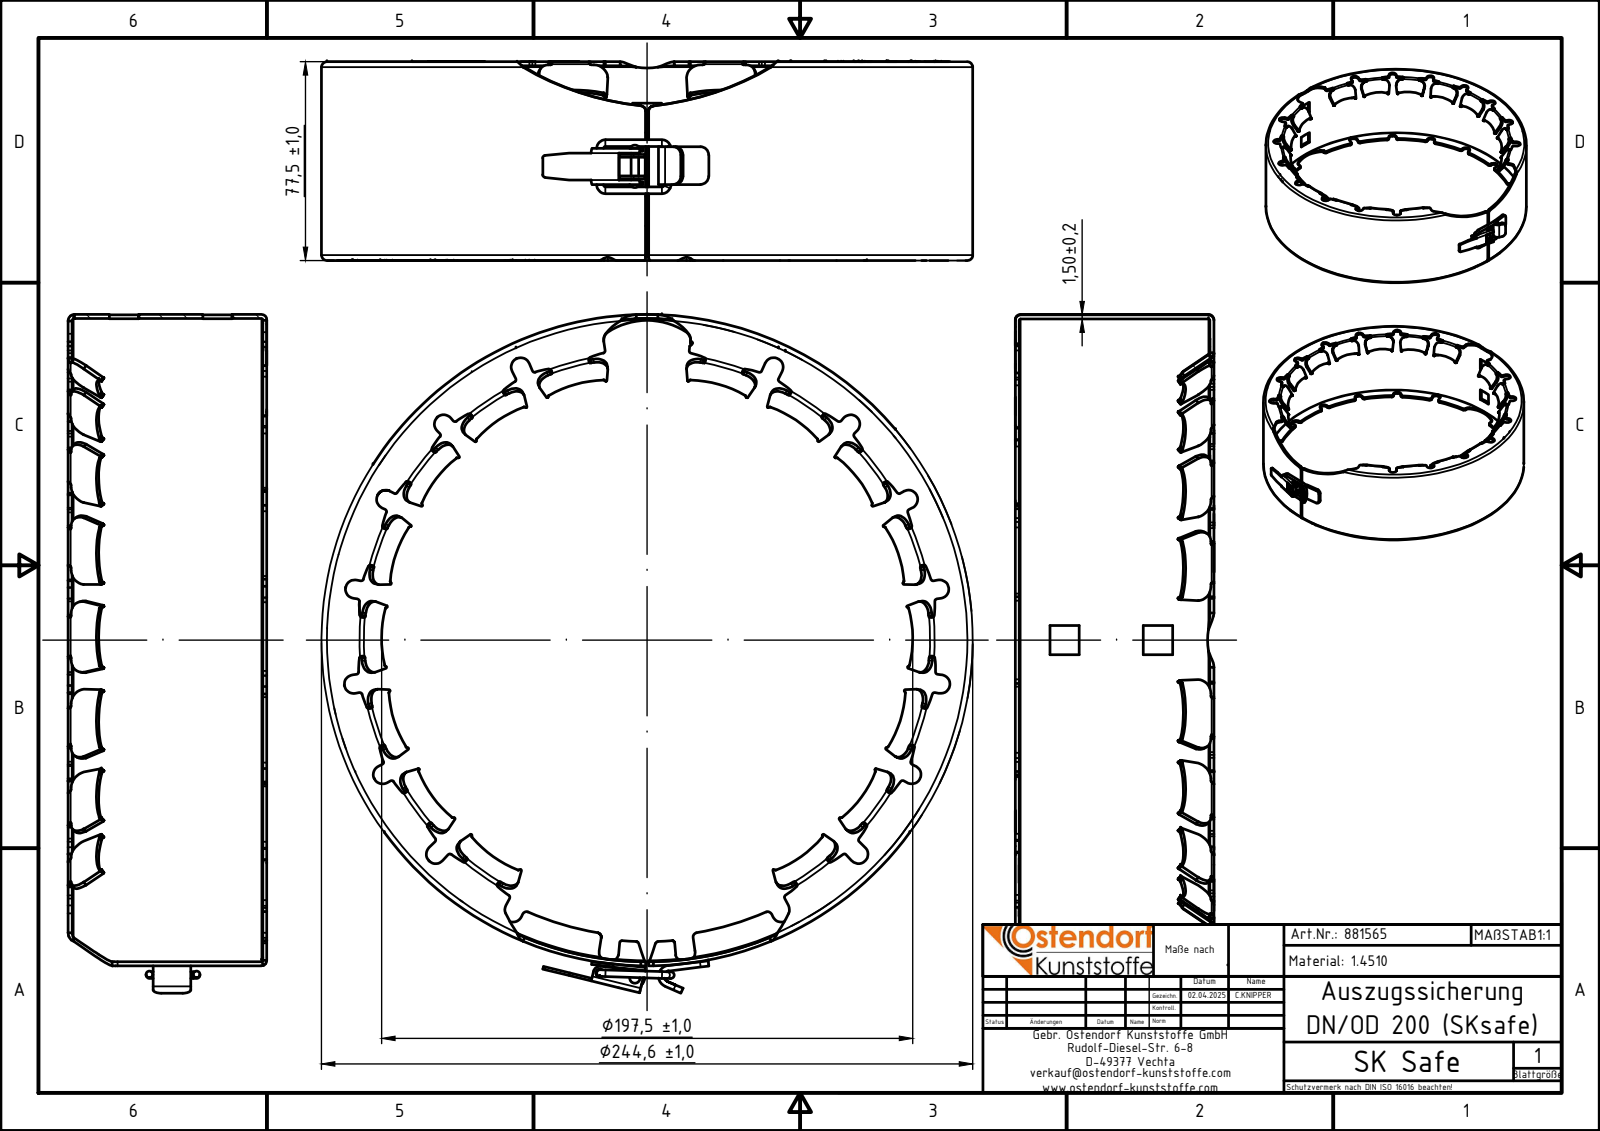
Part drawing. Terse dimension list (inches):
name: 881565z
written by: Autodesk Inventor 2024 (AUTOMOTIVE_DESIGN)
unit: in
bodies: 6 solids, 1093 faces (134 planar, 36 cylindrical, 923 other)
size: 9.92 × 9.52 × 2.904
volume: 6.607 in³; area: 231.2 in²
holes: 3× ⌀0.118
bosses: 3× ⌀0.098, 1× ⌀0.11
rounds: 5× R0.118, 4× R0.039, 2× R0.029, 2× R0.069, 2× R0.138, 1× R0.079, 1× R0.098, 1× R0.143
face distances: 0.039, 0.079, 0.491, 0.315, 0.039, 0.088, 0.404, 0.403, 0.089, 0.059
hole spacings: 0.197, 0.317, 0.515
